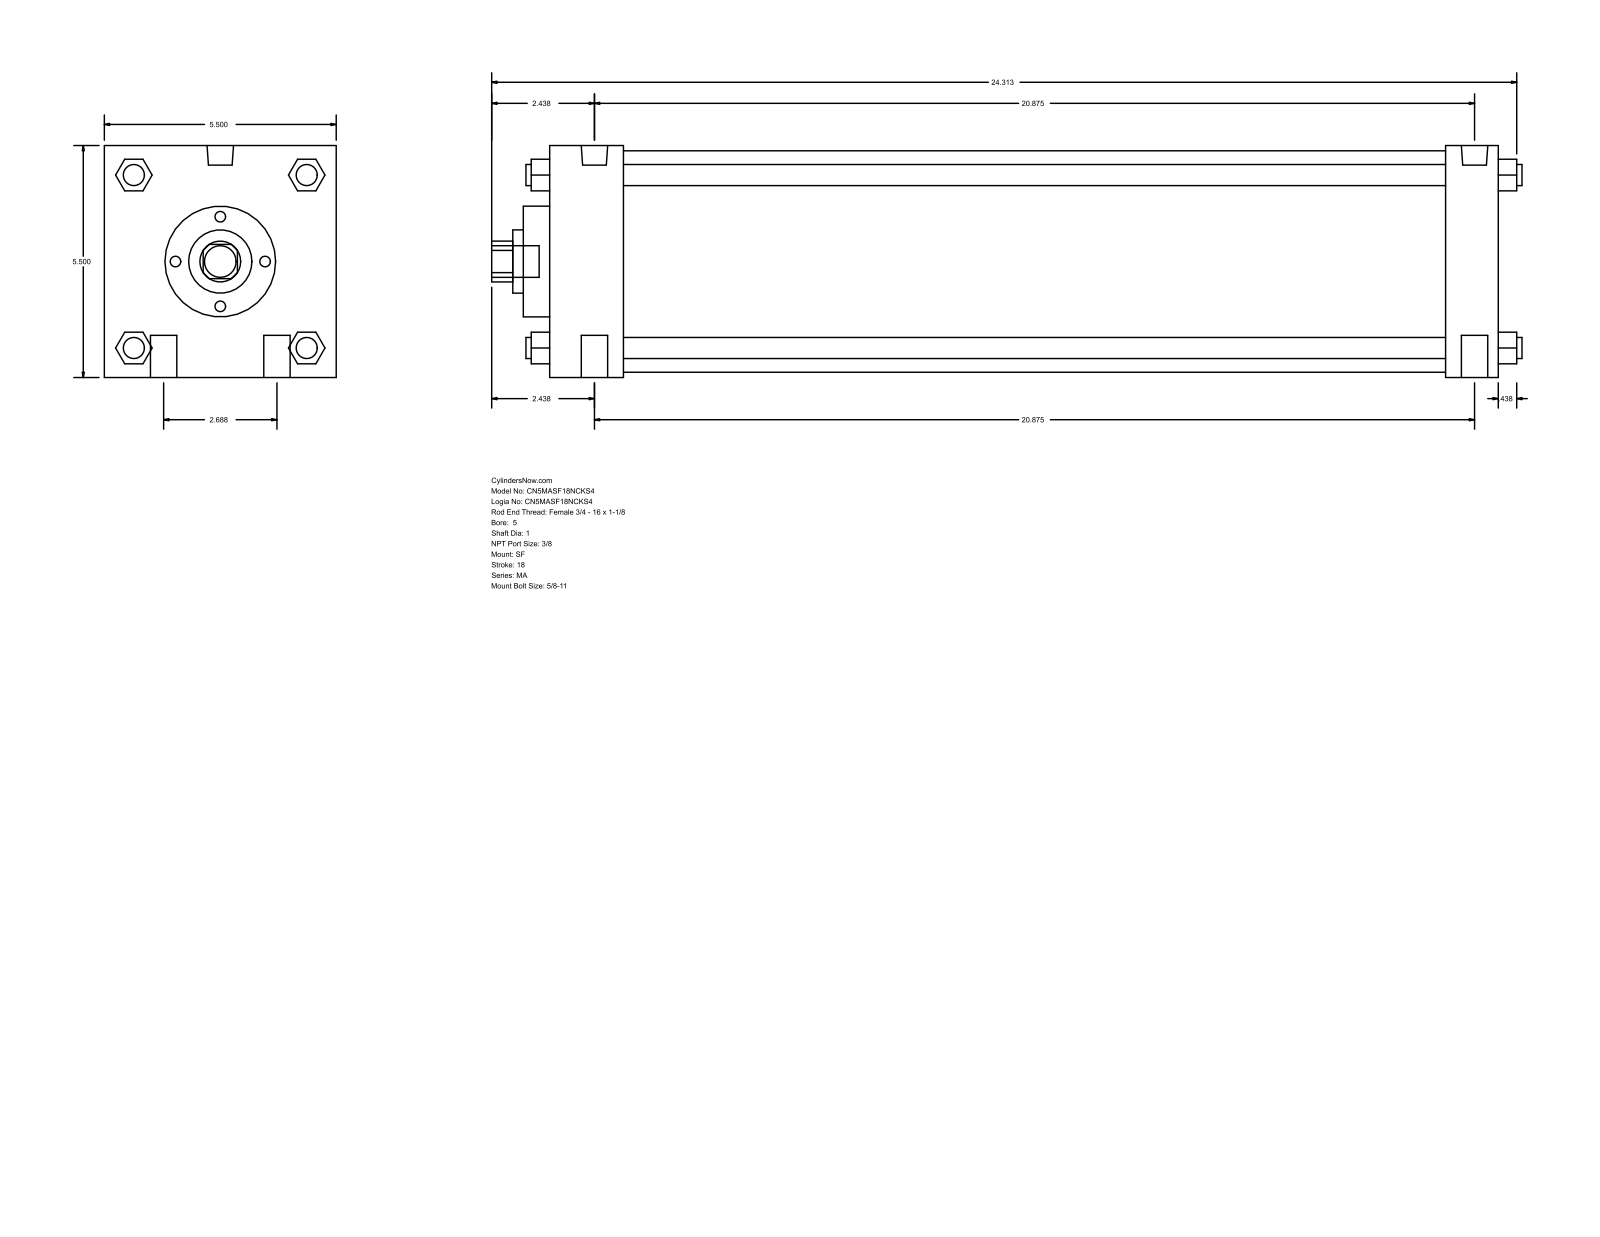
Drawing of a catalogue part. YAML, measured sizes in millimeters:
part_name: "MA_SF__0500_1"
step_written_by: "GSSL Pune (CONFIG_CONTROL_DESIGN)"
units: millimeters
bodies: {solids: 0, faces: 126, planar: 95, cylindrical: 31, other: 0}
overall_size: [620.71, 139.7, 139.7]
round_holes:
  - {diameter: 25.4, count: 1}
  - {diameter: 38.1, count: 1}
  - {diameter: 66.67, count: 1}
  - {diameter: 133.35, count: 1}
round_bosses_or_shafts:
  - {diameter: 15.88, count: 4}
  - {diameter: 12.7, count: 4}
  - {diameter: 15.93, count: 2}
  - {diameter: 11.11, count: 2}
  - {diameter: 19.05, count: 1}
partial_cylinders:
  - {radius: 12.29, count: 1}
face_to_face_distances: [139.7, 571.5, 44.46, 539.75, 495.29, 527.04, 31.75, 15.87, 60.33, 555.62]
